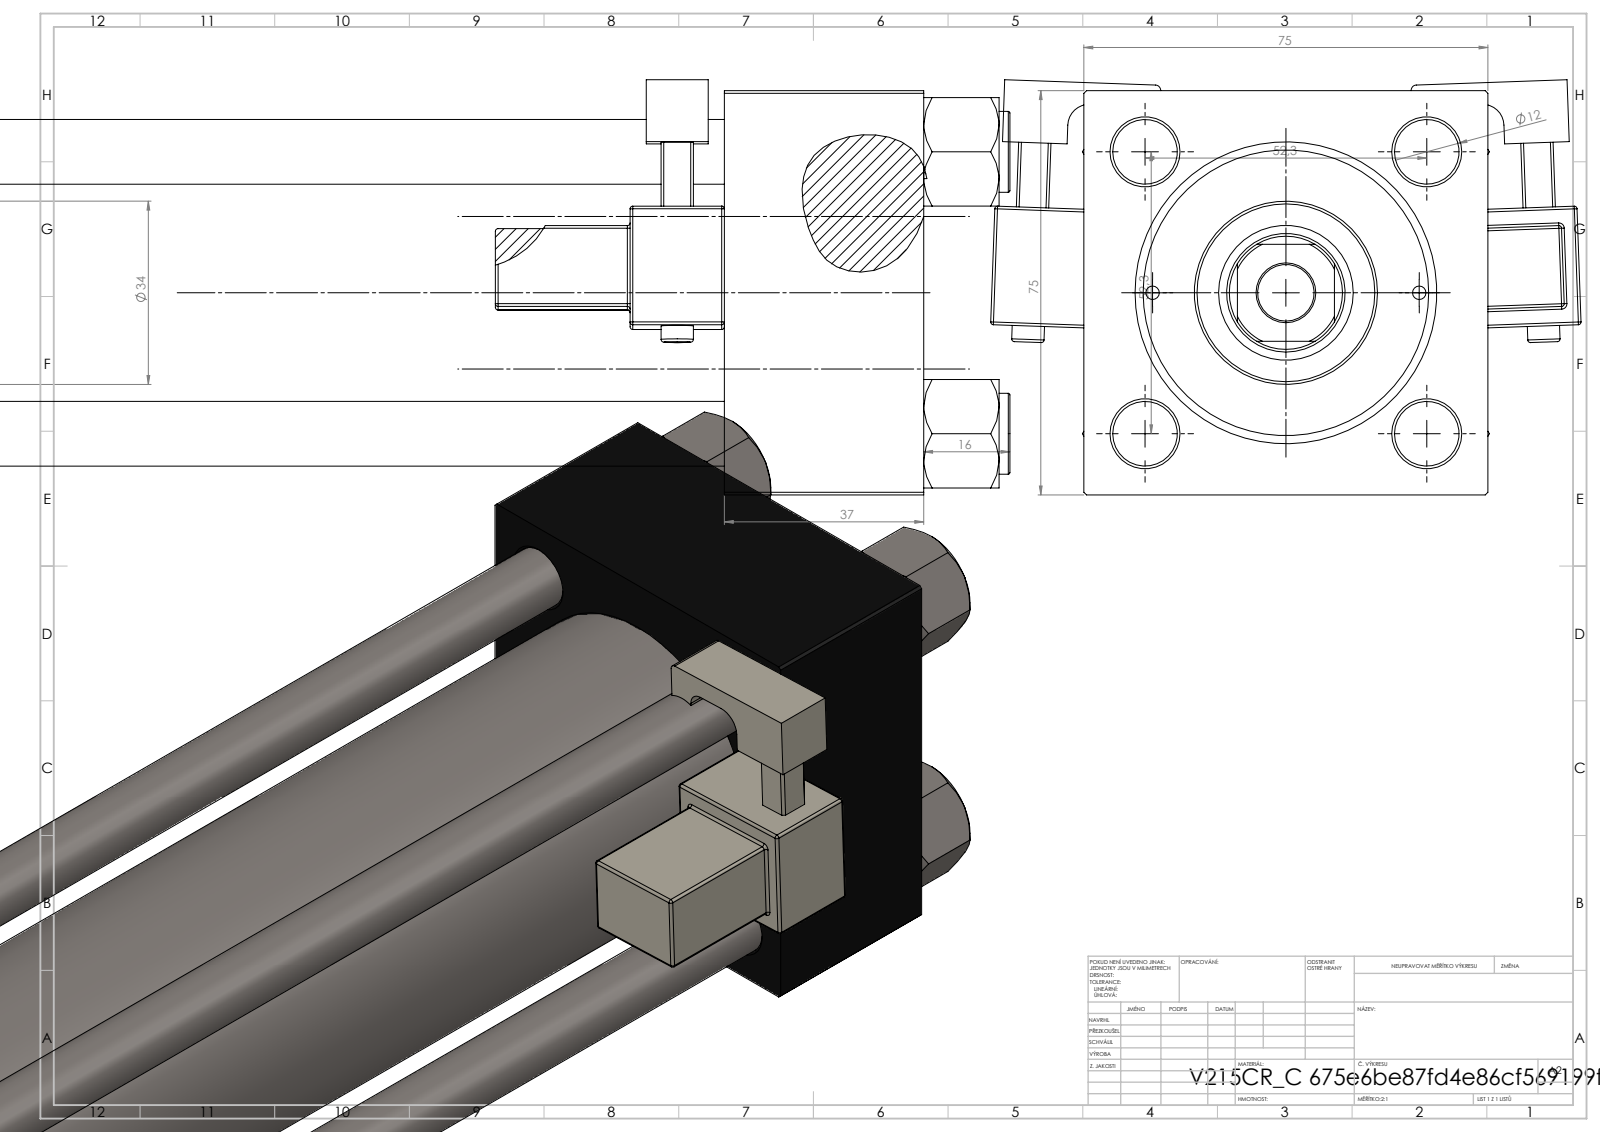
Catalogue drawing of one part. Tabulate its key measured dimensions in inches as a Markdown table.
| quantity | value |
| --- | --- |
| part name | V215CR_MSU; NUT_M5_C; V215CR_C_TYCINKA; V215CR_C_Body (+2 more) |
| STEP written by | SolidWorks 2019 (CONFIG_CONTROL_DESIGN) |
| units | inches |
| bodies | 13 solids, 1308 faces (586 planar, 150 cylindrical, 572 other) |
| overall size | 14.764 × 4.314 × 3.033 |
| volume | 57.23 in³ |
| surface area | 401.7 in² |
| round holes (diameter × count) | 0.472 × 4, 0.098 × 2, 0.276 × 2, 0.825 × 2, 1.181 × 2, 0.413 × 1, 0.866 × 1, 0.984 × 1, 1.614 × 1, 1.969 × 1, 2.087 × 1 |
| round bosses / shafts (diameter × count) | 0.591 × 4, 0.236 × 2, 2.205 × 1, 1.339 × 1 |
| partial cylindrical surfaces (radius × count) | 0.02 × 48, 0.039 × 2, 0.098 × 2, 0.157 × 2, 0.413 × 1 |
| main face-to-face distances | 2.953, 1.457, 13.15, 11.693, 10.827, 9.37, 2.323, 12.02, 10.563, 1.193 |
| hole center spacings | 1.031, 1.456, 2.059, 2.253, 0.974, 2.912, 1.949, 10.768 |
